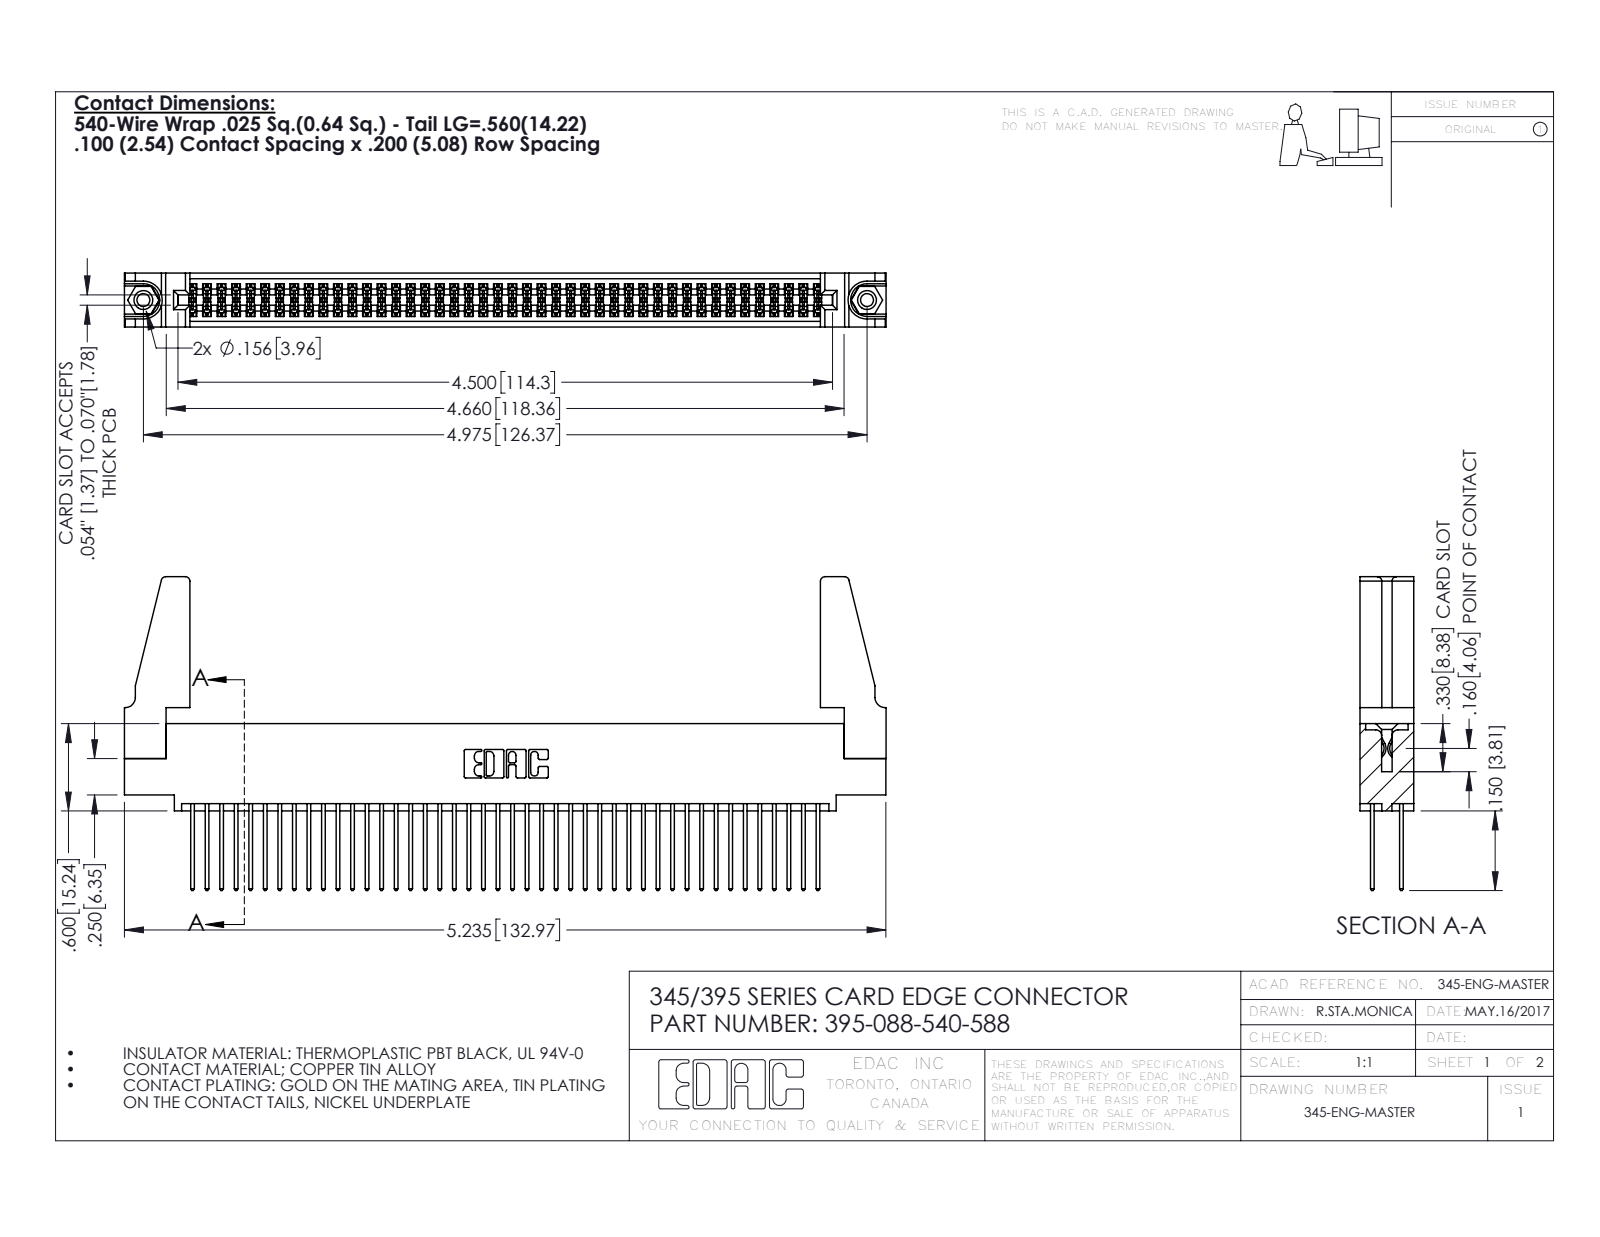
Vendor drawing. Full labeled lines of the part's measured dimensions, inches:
Part name (STEP PRODUCT): 345 Part_0.110 Offset - 0.156 Dia-TH; 395-088-540-588; 345-250-001_345-250-001-102; 345-292-001_345-293-140 (+1 more)
STEP written by: SolidWorks 2016 (CONFIG_CONTROL_DESIGN)
Units: inches
Bodies: 93 solids, 4654 faces (3060 planar, 1578 cylindrical, 16 other)
Overall size (bounding box): 5.236 × 2.157 × 0.37
Volume: 1.004 in³ · Surface area: 37.68 in²
Round holes (diameter × count): ⌀0.089 ×2, ⌀0.125 ×2, ⌀0.156 ×2, ⌀0.064 ×1
Round bosses / shafts (diameter × count): ⌀0.155 ×2
Partial cylindrical surfaces — rounded edges, fillets, slot ends (radius × count): R0.006 ×132, R0.01 ×88, R0.01 ×22, R0.03 ×8, R0.007 ×6, R0.031 ×6, R0.026 ×3, R0.014 ×2
Main face-to-face distances: 0.072, 0.298, 0.2, 0.098, 0.272, 0.025, 0.37, 0.225, 0.175, 0.149
Hole centre spacings: 0.27, 4.739, 4.975
